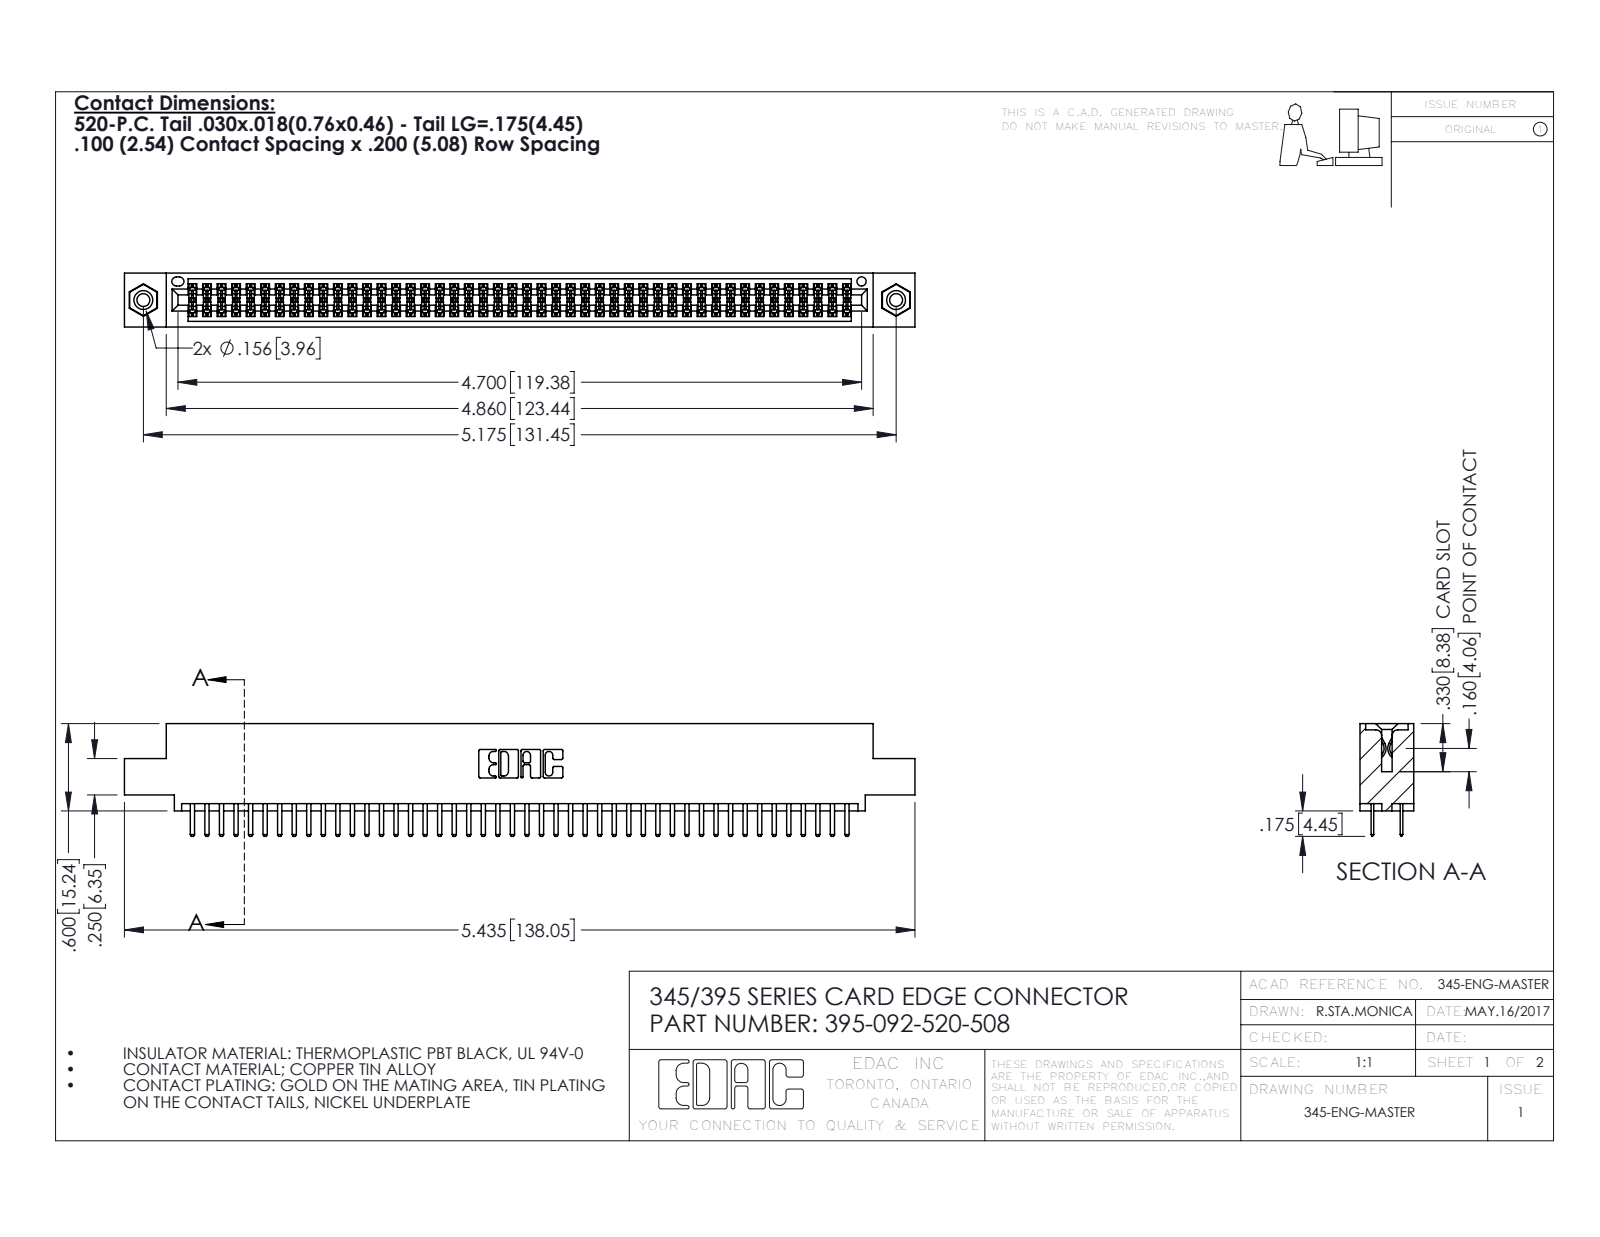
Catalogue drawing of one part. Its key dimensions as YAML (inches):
part_name: "395-092-520-508; 345-292-001_345-293-120; 345-250-001_345-250-003-102; 345 Part_0.110 Offset - 0.156 Dia-TI"
step_written_by: "SolidWorks 2016 (CONFIG_CONTROL_DESIGN)"
units: inches
bodies: {solids: 95, faces: 5158, planar: 3336, cylindrical: 1806, other: 16}
overall_size: [5.435, 0.775, 0.37]
volume: 0.813
surface_area: 30.69
round_holes:
  - {diameter: 0.089, count: 2}
  - {diameter: 0.125, count: 2}
  - {diameter: 0.156, count: 2}
  - {diameter: 0.064, count: 1}
round_bosses_or_shafts:
  - {diameter: 0.155, count: 2}
partial_cylinders:
  - {radius: 0.006, count: 138}
  - {radius: 0.01, count: 96}
  - {radius: 0.01, count: 22}
  - {radius: 0.007, count: 6}
  - {radius: 0.031, count: 6}
  - {radius: 0.026, count: 3}
  - {radius: 0.014, count: 2}
  - {radius: 0.019, count: 2}
face_to_face_distances: [0.072, 0.298, 0.2, 0.37, 0.098, 0.272, 0.025, 0.225, 0.022, 0.072]
hole_center_spacings: [0.27, 4.939, 5.175]
